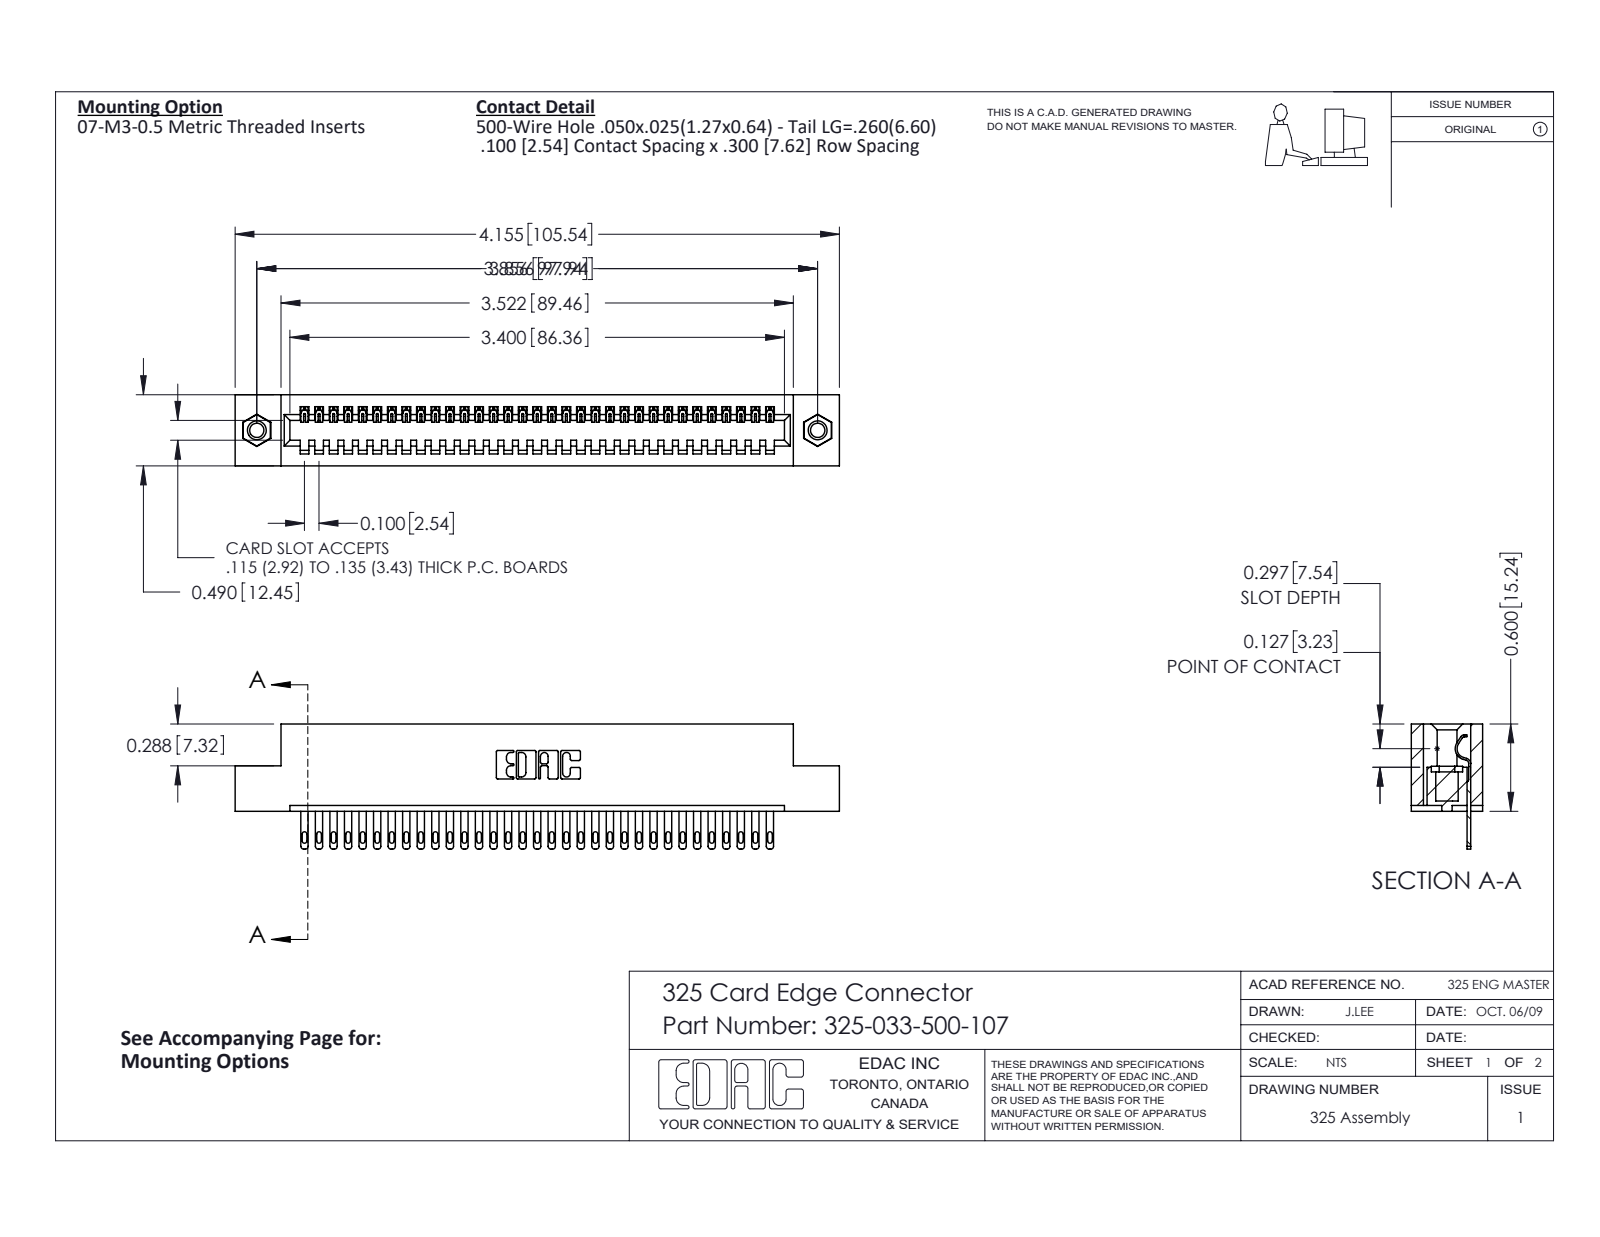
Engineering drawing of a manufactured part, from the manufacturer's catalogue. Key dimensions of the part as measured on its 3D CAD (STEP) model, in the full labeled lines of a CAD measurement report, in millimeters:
Part name (STEP PRODUCT): 345-250-001_345-250-005-103; 325 Part_TI; 325-292-001_325-293-100; 325-033-500-107
STEP written by: SolidWorks 2016 (CONFIG_CONTROL_DESIGN)
Units: millimetres
Bodies: 36 solids, 1956 faces (1290 planar, 650 cylindrical, 16 other)
Overall size (bounding box): 105.5 × 21.8 × 12.4
Volume: 13 300 mm³ · Surface area: 14 520 mm²
Round holes (diameter × count): ⌀2.5 ×2, ⌀3.2 ×2, ⌀4.1 ×2
Round bosses / shafts (diameter × count): ⌀3.9 ×2
Partial cylindrical surfaces — rounded edges, fillets, slot ends (radius × count): R0.2 ×66, R0.4 ×66, R0.5 ×66, R0.3 ×22, R0.2 ×6, R0.8 ×6, R0.7 ×3, R0.4 ×1
Main face-to-face distances: 2.1, 10.3, 12.4, 7.6, 2.7, 9.7, 0.6, 8.3, 14.2, 1
Hole centre spacings: 97.9
